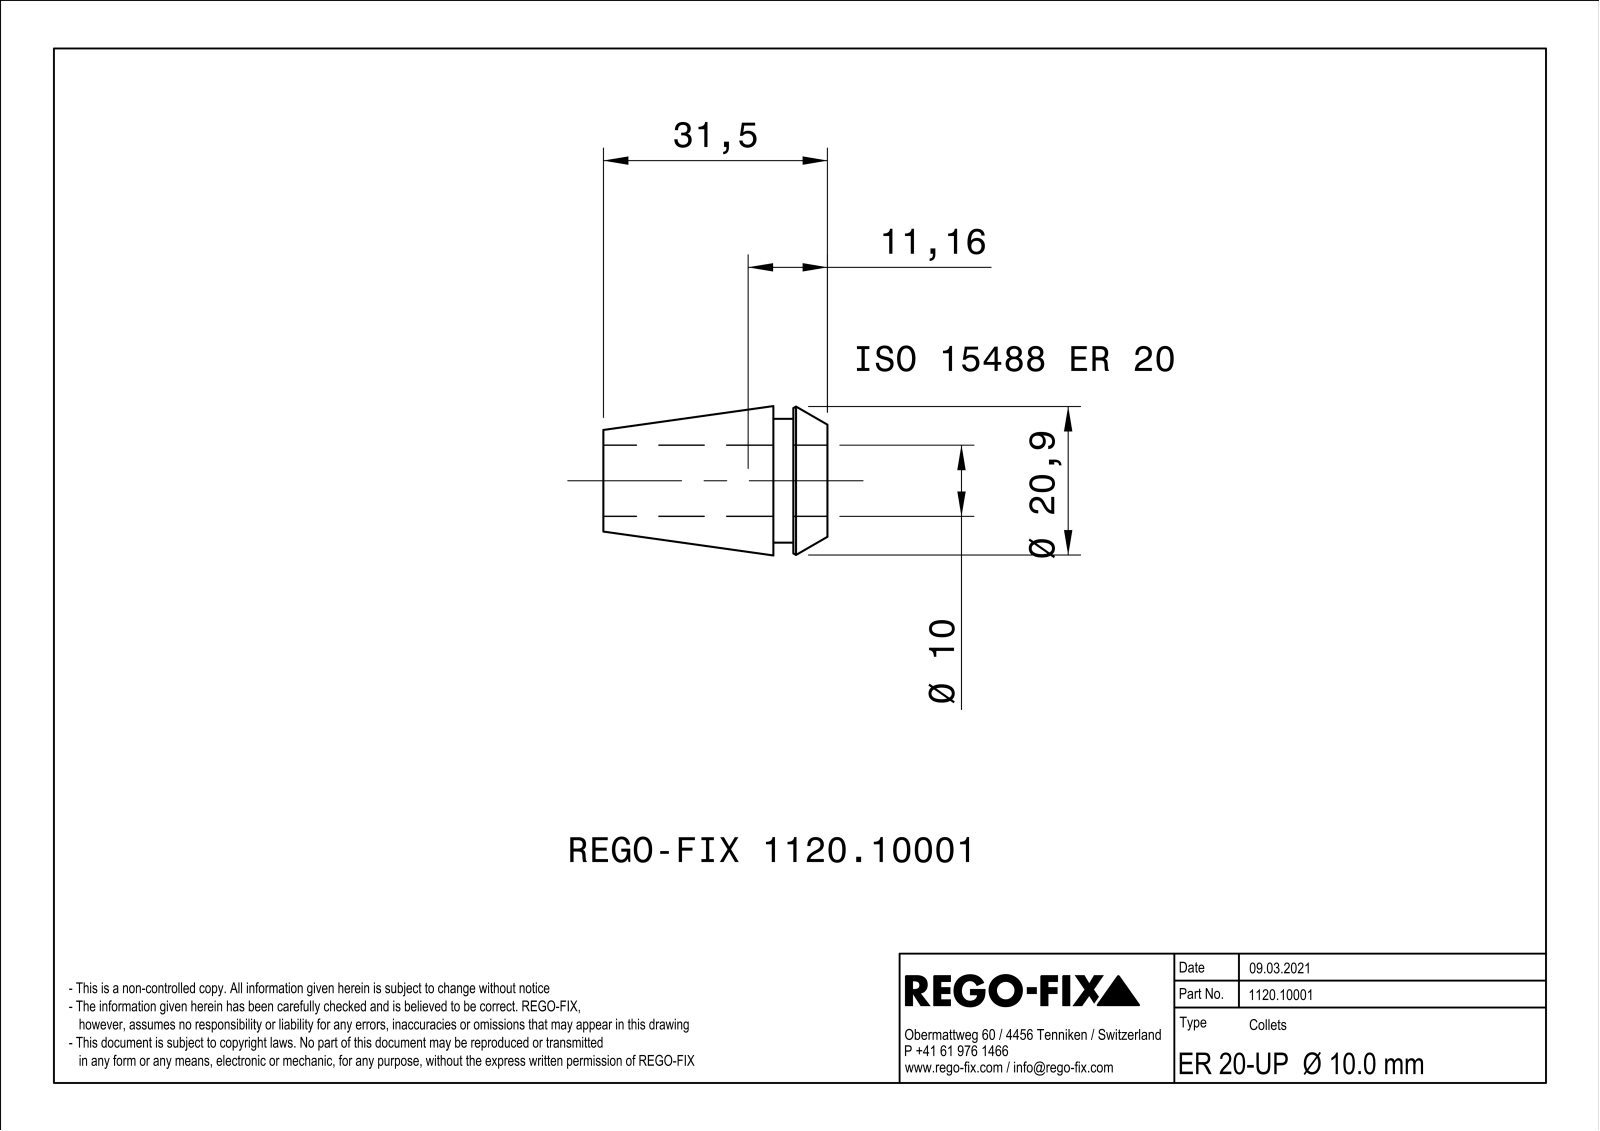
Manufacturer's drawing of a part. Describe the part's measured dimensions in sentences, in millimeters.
The part is named "NOCUT". Its 3-D file was written by "SIEMENS PLM Software Solid Edge ST10 (AUTOMOTIVE_DESIGN)". It is 1 solid with 177 faces: 88 planar, 9 cylindrical and 80 other. Overall it measures 31.5 by 20.99 by 20.99 millimeters. Its volume is 4 368 cubic millimeters and its surface area 6 077 square millimeters. Round holes: 1 of diameter 10. Round bosses or shafts: 1 of diameter 17.4. The main face-to-face distances are 0.6, 7.6, 4.8, 2.8, 31.5, 26.7, 23.9, 5.5, 0.7, 2.1.
